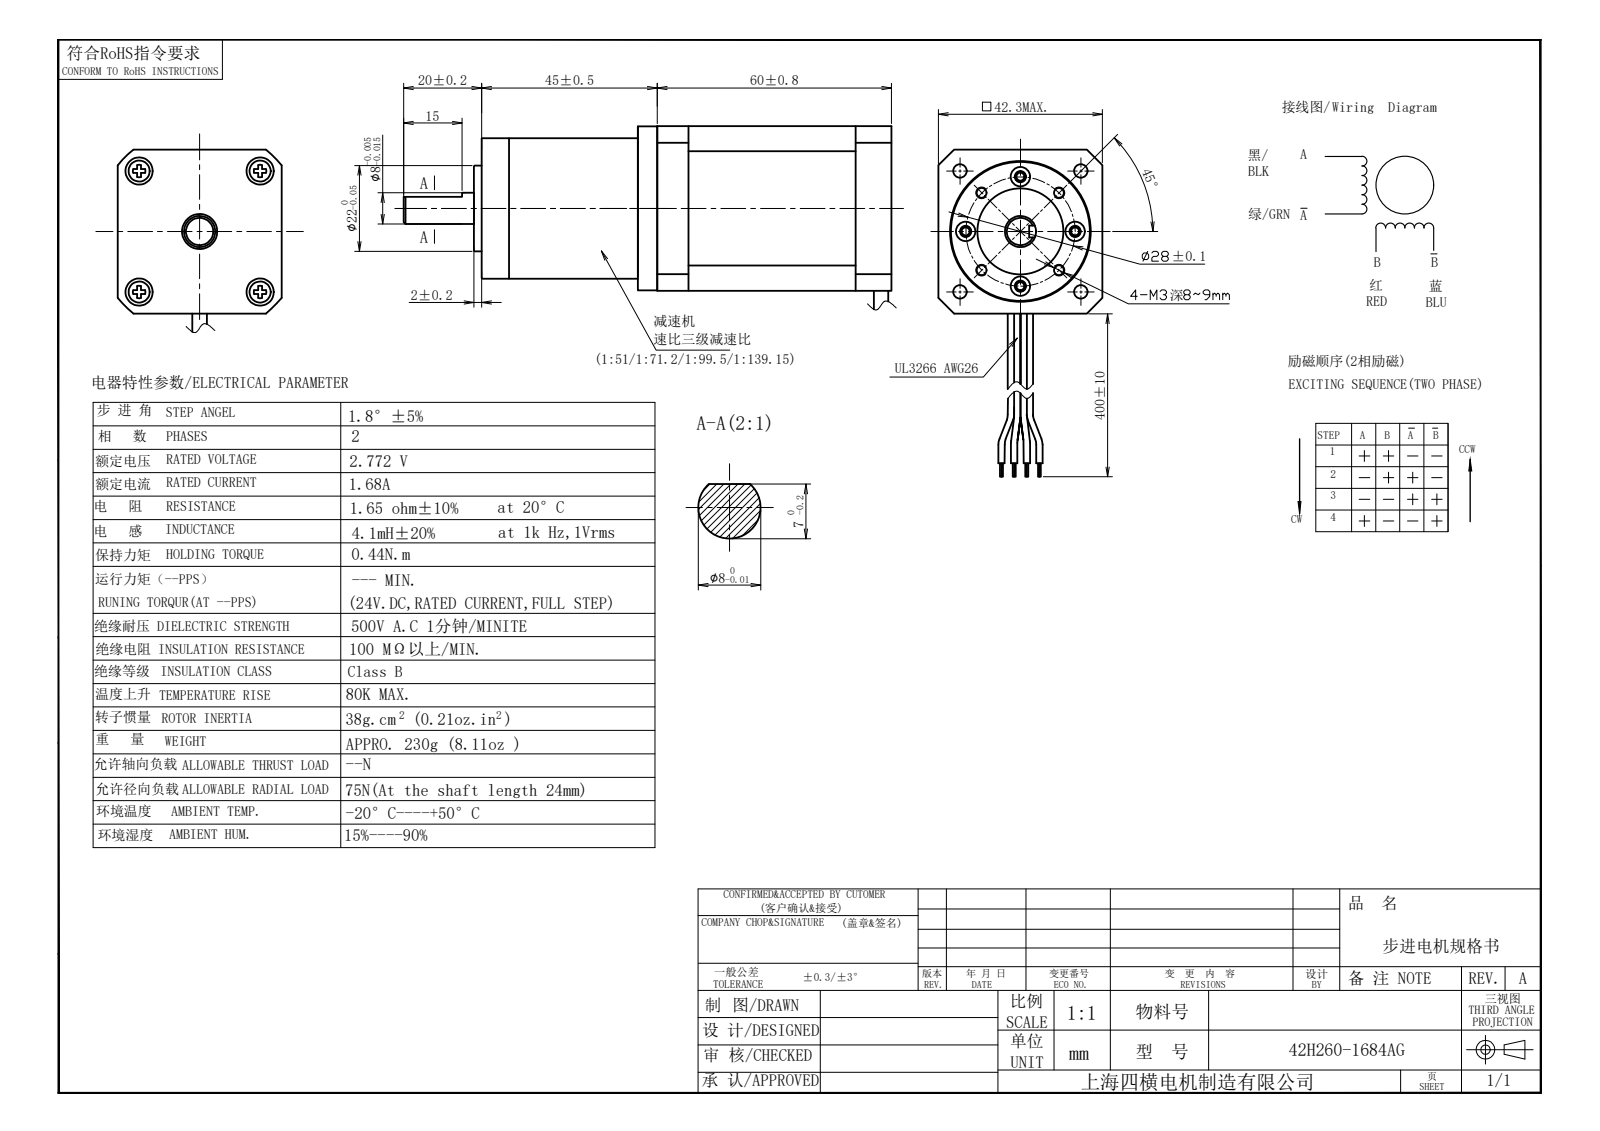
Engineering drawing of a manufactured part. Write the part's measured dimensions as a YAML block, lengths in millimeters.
part_name: "hexagon socket head cap screws gb_GB_FASTENER_SCREWS_HSHCS M3X6-N; PLA36-003前端盖; 42A-D19; 698ZZ 19x8x6 (+8 more)"
step_written_by: "SolidWorks 2020 (CONFIG_CONTROL_DESIGN)"
units: millimeters
bodies: {solids: 22, faces: 898, planar: 198, cylindrical: 559, other: 141}
overall_size: [125, 82.75, 42.3]
volume: 134038
surface_area: 50134
round_holes:
  - {diameter: 2.5, count: 8}
  - {diameter: 3.5, count: 5}
  - {diameter: 2.05, count: 4}
  - {diameter: 2.9, count: 4}
  - {diameter: 3.3, count: 4}
  - {diameter: 3.4, count: 4}
  - {diameter: 5, count: 4}
  - {diameter: 5.5, count: 4}
  - {diameter: 3, count: 3}
  - {diameter: 1.2, count: 2}
  - {diameter: 7.4, count: 1}
  - {diameter: 8, count: 1}
round_bosses_or_shafts:
  - {diameter: 5, count: 4}
  - {diameter: 3, count: 4}
  - {diameter: 1.4, count: 4}
  - {diameter: 36, count: 1}
  - {diameter: 25.9, count: 1}
  - {diameter: 22, count: 1}
  - {diameter: 21.9, count: 1}
  - {diameter: 21.5, count: 1}
partial_cylinders:
  - {radius: 0.2, count: 92}
  - {radius: 2.8, count: 92}
  - {radius: 0.41, count: 8}
  - {radius: 0.44, count: 8}
  - {radius: 0.3, count: 6}
  - {radius: 3, count: 2}
  - {radius: 4.75, count: 1}
  - {radius: 6, count: 1}
face_to_face_distances: [42.3, 43, 8, 5, 51, 9, 13, 56, 60, 65]
hole_center_spacings: [10.72, 14, 15.57, 19.8, 25.87, 26.01, 33.32, 7.92]
